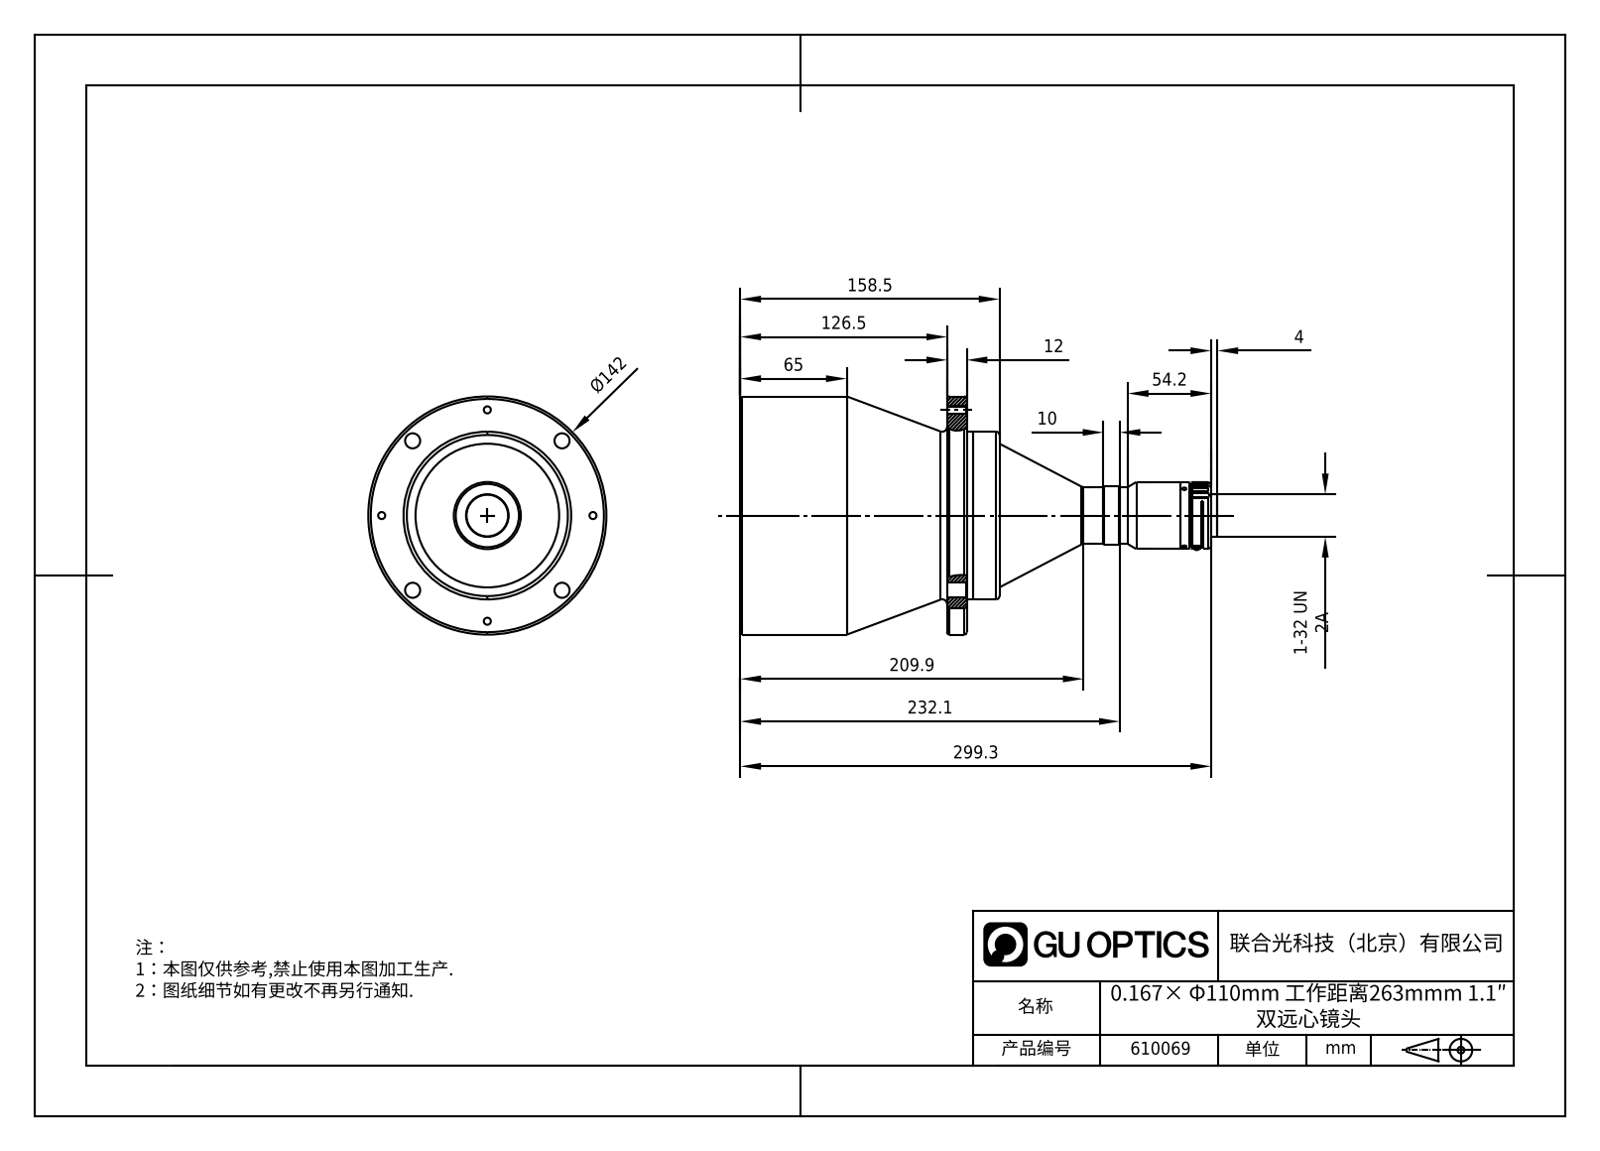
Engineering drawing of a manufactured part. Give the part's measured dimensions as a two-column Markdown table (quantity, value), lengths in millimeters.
| quantity | value |
| --- | --- |
| part name | DTCM111-110-AL |
| STEP written by | SolidWorks 2017 (CONFIG_CONTROL_DESIGN) |
| units | millimeters |
| bodies | 1 solid, 86 faces (8 planar, 42 cylindrical, 36 other) |
| overall size | 303.3 × 142 × 142 |
| volume | 2 327 000 mm³ |
| surface area | 122 796 mm² |
| round holes (diameter × count) | 4.2 × 4, 9 × 4, 2.5 × 3 |
| round bosses / shafts (diameter × count) | 142 × 1, 100 × 1, 40 × 1, 35 × 1, 34 × 1, 33 × 1, 25.4 × 1 |
| main face-to-face distances | 138.5, 126.5, 12, 158.5, 32, 20, 299.3, 172.8, 160.8, 140.8 |
| hole center spacings | 48.22, 89.1, 116.41, 126, 126.01 |
